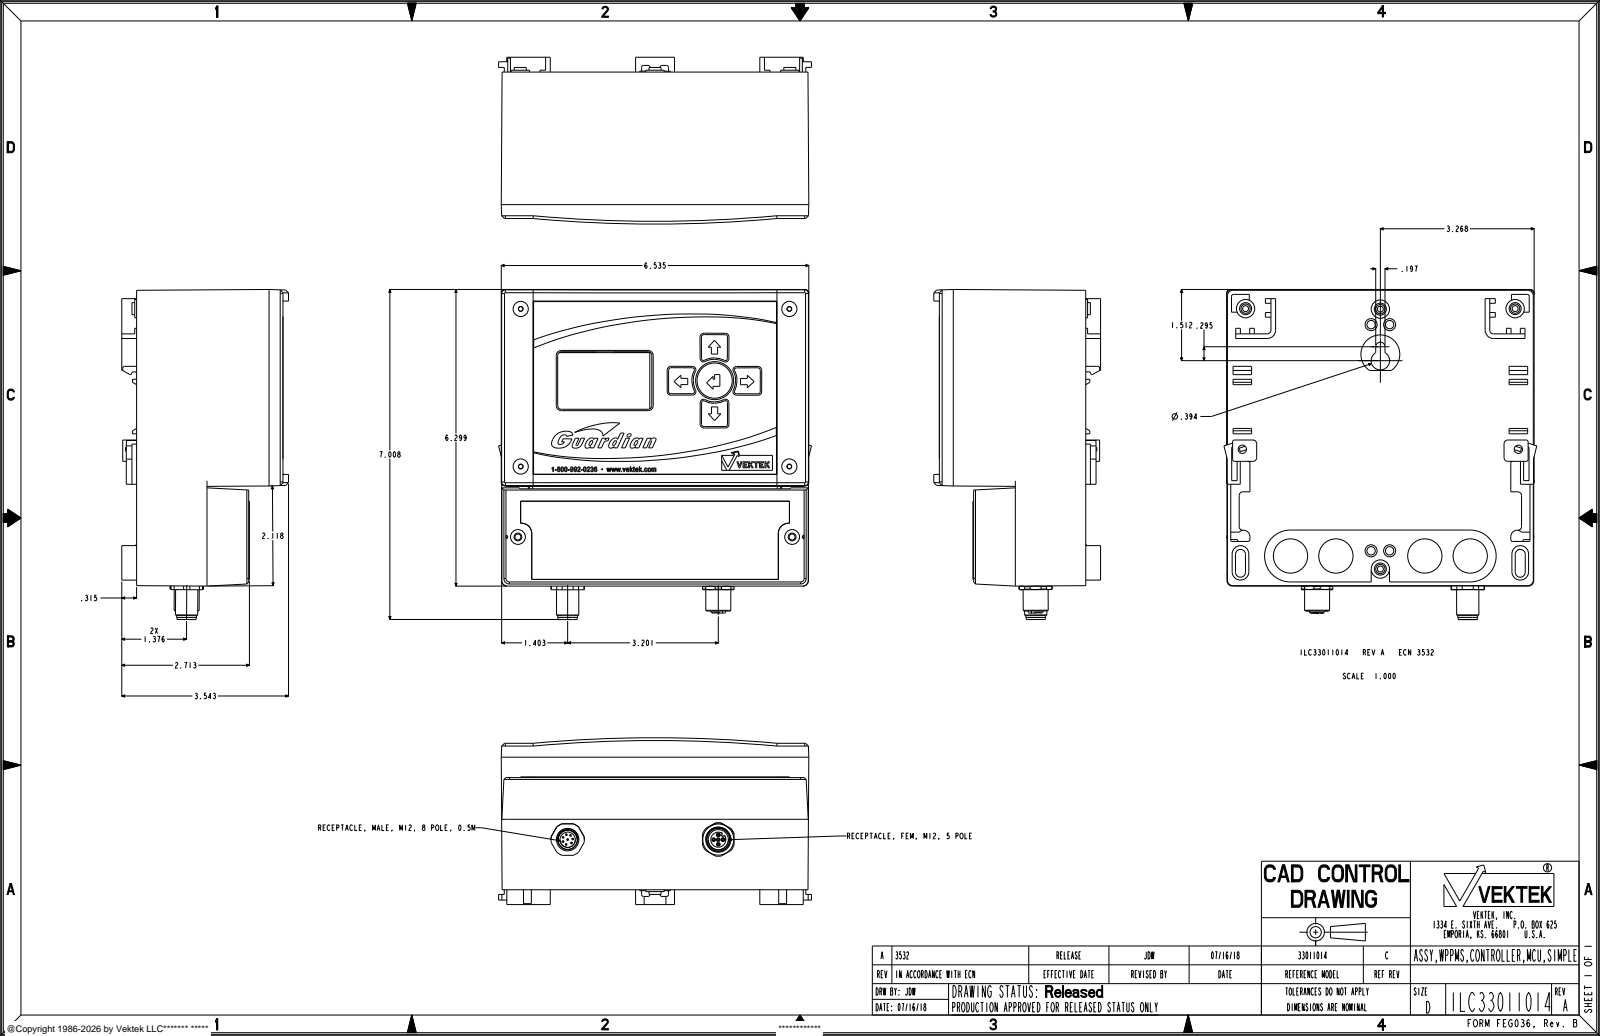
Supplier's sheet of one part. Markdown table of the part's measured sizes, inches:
| quantity | value |
| --- | --- |
| part name | ILC33011014 |
| STEP written by | PRO/ENGINEER BY PARAMETRIC TECHNOLOGY CORPORATION, 2013320 (AUTOMOTIVE_DESIGN) |
| units | inches |
| bodies | 1 solid, 2511 faces (1354 planar, 466 cylindrical, 691 other) |
| overall size | 7.01 × 6.648 × 3.543 |
| volume | 25.98 in³ |
| surface area | 463.4 in² |
| round holes (diameter × count) | 0.126 × 16, 0.094 × 14, 0.102 × 14, 0.125 × 8, 0.043 × 5, 0.118 × 4, 0.197 × 4, 0.323 × 4, 0.728 × 4, 0.165 × 2, 0.177 × 2, 0.315 × 2 |
| round bosses / shafts (diameter × count) | 0.354 × 18, 0.236 × 10, 0.256 × 8, 0.032 × 8, 0.079 × 5, 0.055 × 5, 0.39 × 4, 0.232 × 4 |
| partial cylindrical surfaces (radius × count) | 0.079 × 18, 0.177 × 14, 0.039 × 9, 0.118 × 8, 0.008 × 6, 0.02 × 4, 0.063 × 4, 0.106 × 4 |
| main face-to-face distances | 0.062, 2.139, 0.118, 2.201, 0.433, 0.495, 0.377, 0.315, 2.572, 2.454 |
| hole center spacings | 0.098, 0.769, 3.285, 5.709, 5.81, 6.145, 0.502, 1.65 |
